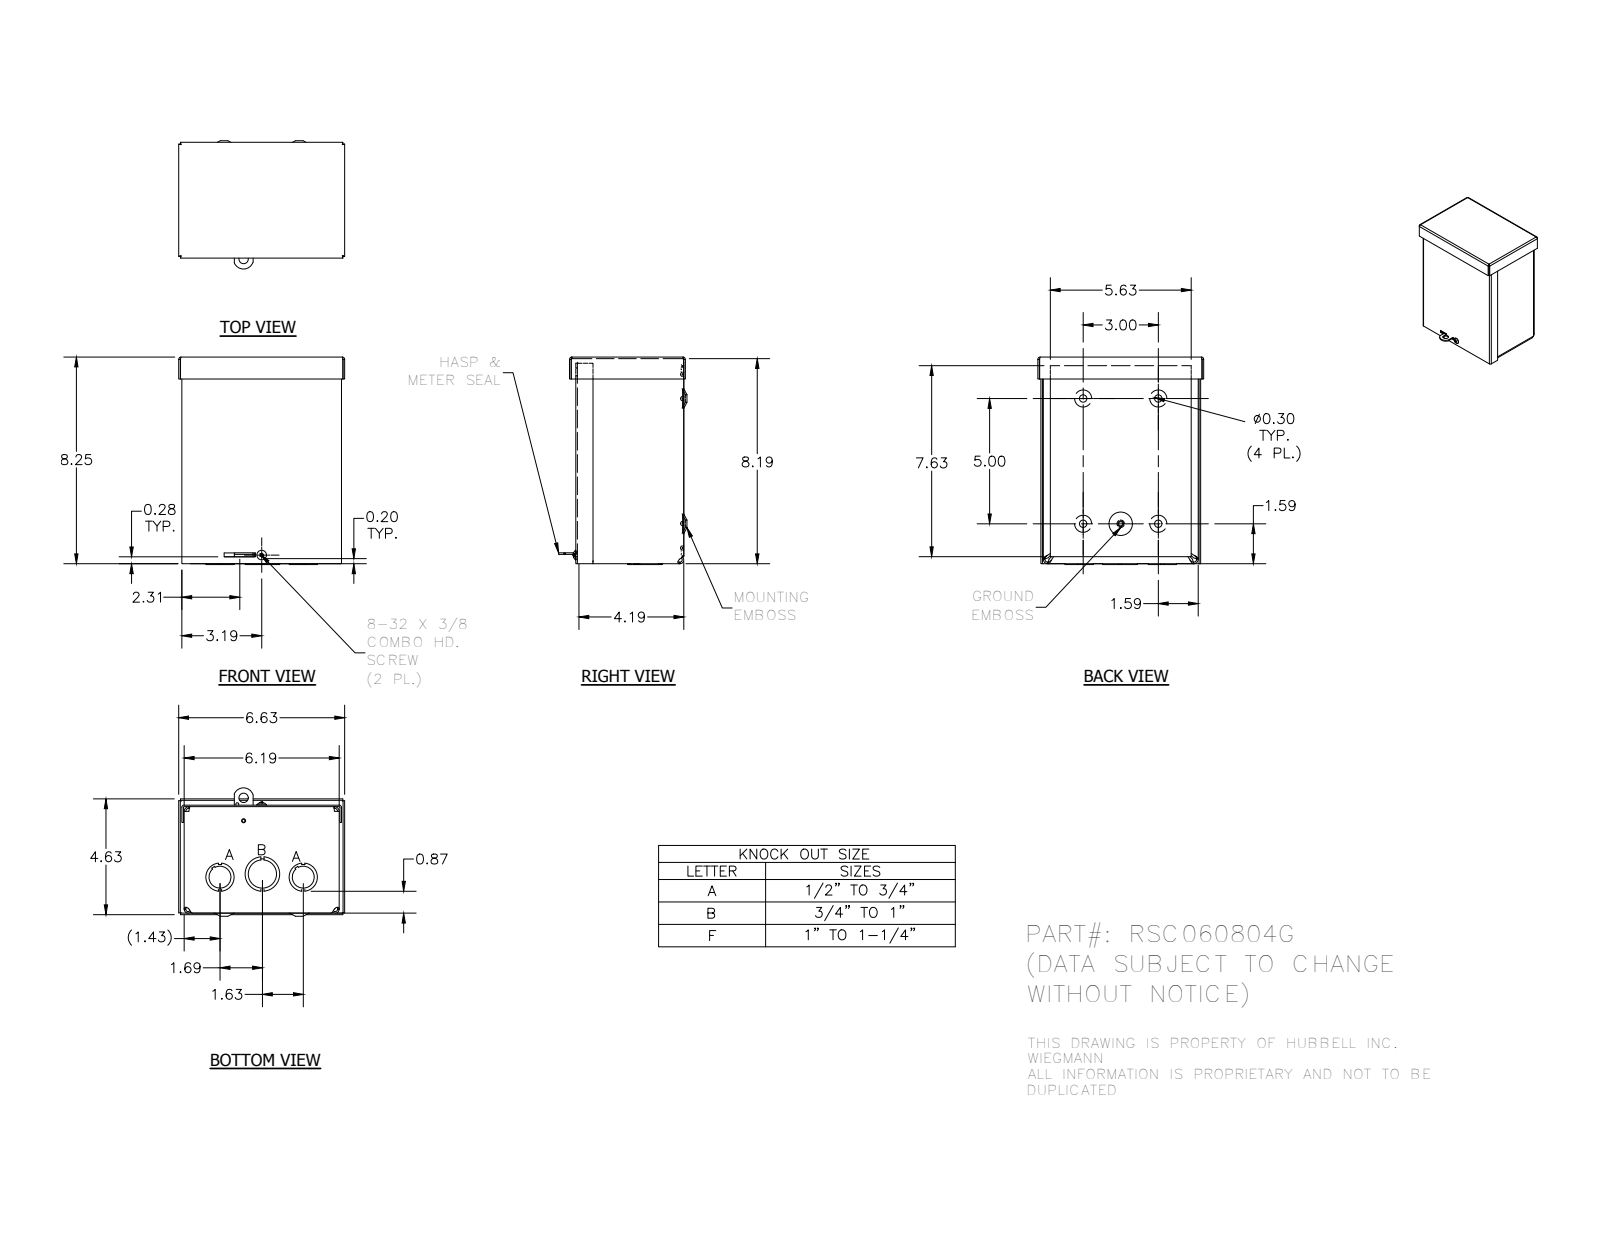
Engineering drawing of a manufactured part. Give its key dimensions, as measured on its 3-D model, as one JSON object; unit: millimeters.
{"part_name": "RSC060804G_WRAP; RSC0608G_LID; RSC0604G_CAP; 3183 (+4 more)", "step_written_by": "Autodesk Inventor 2014 (AUTOMOTIVE_DESIGN)", "units": "millimeters", "bodies": {"solids": 6, "faces": 461, "planar": 220, "cylindrical": 116, "other": 125}, "overall_size": [210.32, 168.28, 130.17], "volume_mm3": 313028, "surface_area_mm2": 405548, "round_holes": [[7.62, 4], [28.57, 3], [3.17, 2], [7.95, 2], [22.22, 2], [3.76, 1], [3.96, 1], [4.19, 1], [9.52, 1], [34.92, 1]], "round_bosses_or_shafts": [[9.75, 1], [5.8, 1], [4.17, 1]], "partial_cylinders_radius": [[0.25, 10], [0.79, 8], [2.37, 8], [3.17, 8], [4.75, 8], [0.53, 4], [0.79, 4], [1.4, 4]], "face_to_face_distances": [1.58, 1.57, 155.59, 107.93, 106.35, 1.59, 206.39, 3.15, 109.52, 107.94], "hole_center_spacings": [38.1, 76.2, 127, 132.58, 148.11, 9.1, 17.84, 23.19]}
